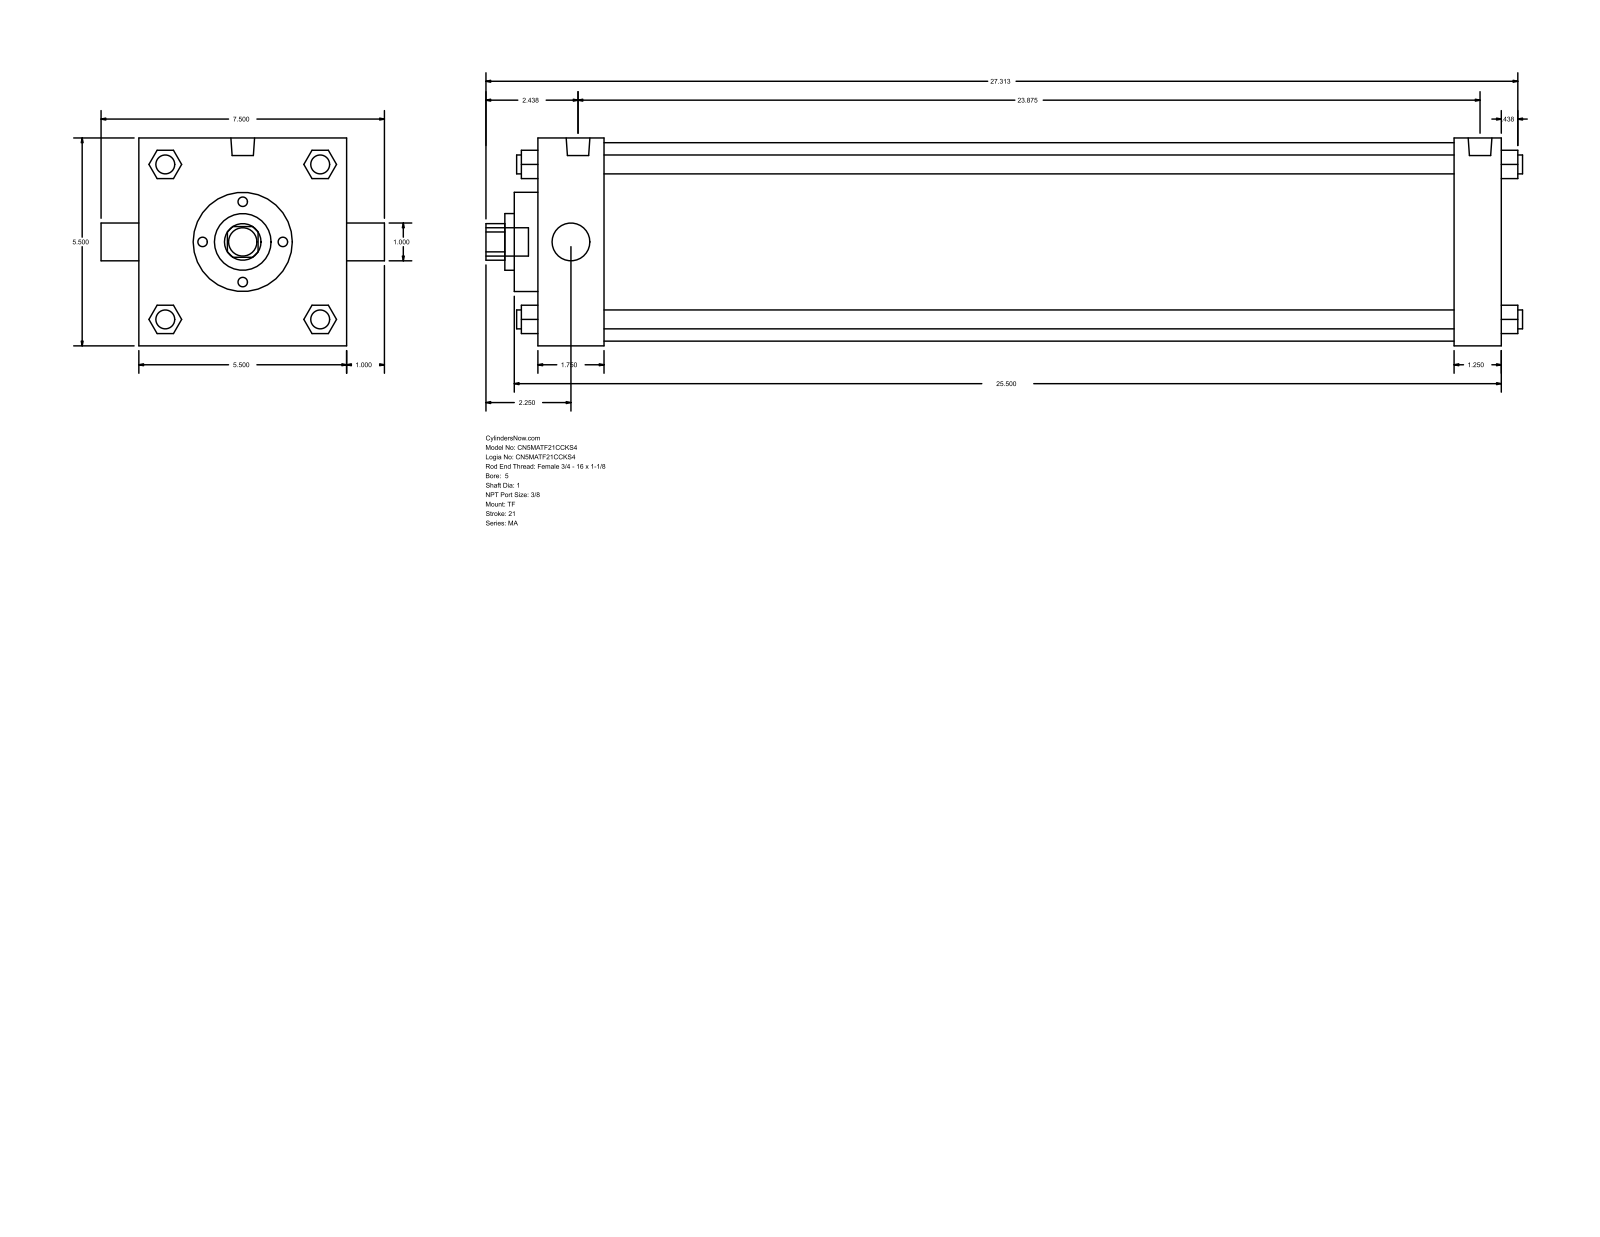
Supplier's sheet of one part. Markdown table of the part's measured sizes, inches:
| quantity | value |
| --- | --- |
| part name | MA_TF__0500_1 |
| STEP written by | GSSL Pune (CONFIG_CONTROL_DESIGN) |
| units | inches |
| bodies | 0 solids, 122 faces (93 planar, 29 cylindrical, 0 other) |
| overall size | 27.437 × 7.5 × 5.5 |
| round holes (diameter × count) | 1 × 2, 1.5 × 1, 2.625 × 1, 5.25 × 1 |
| round bosses / shafts (diameter × count) | 0.5 × 4, 0.437 × 3, 0.627 × 2, 0.75 × 1 |
| partial cylindrical surfaces (radius × count) | 0.484 × 1 |
| main face-to-face distances | 5.5, 25.5, 24.25, 1.25, 1.75, 22.5, 23.75, 0.625, 2.375, 24.875 |
